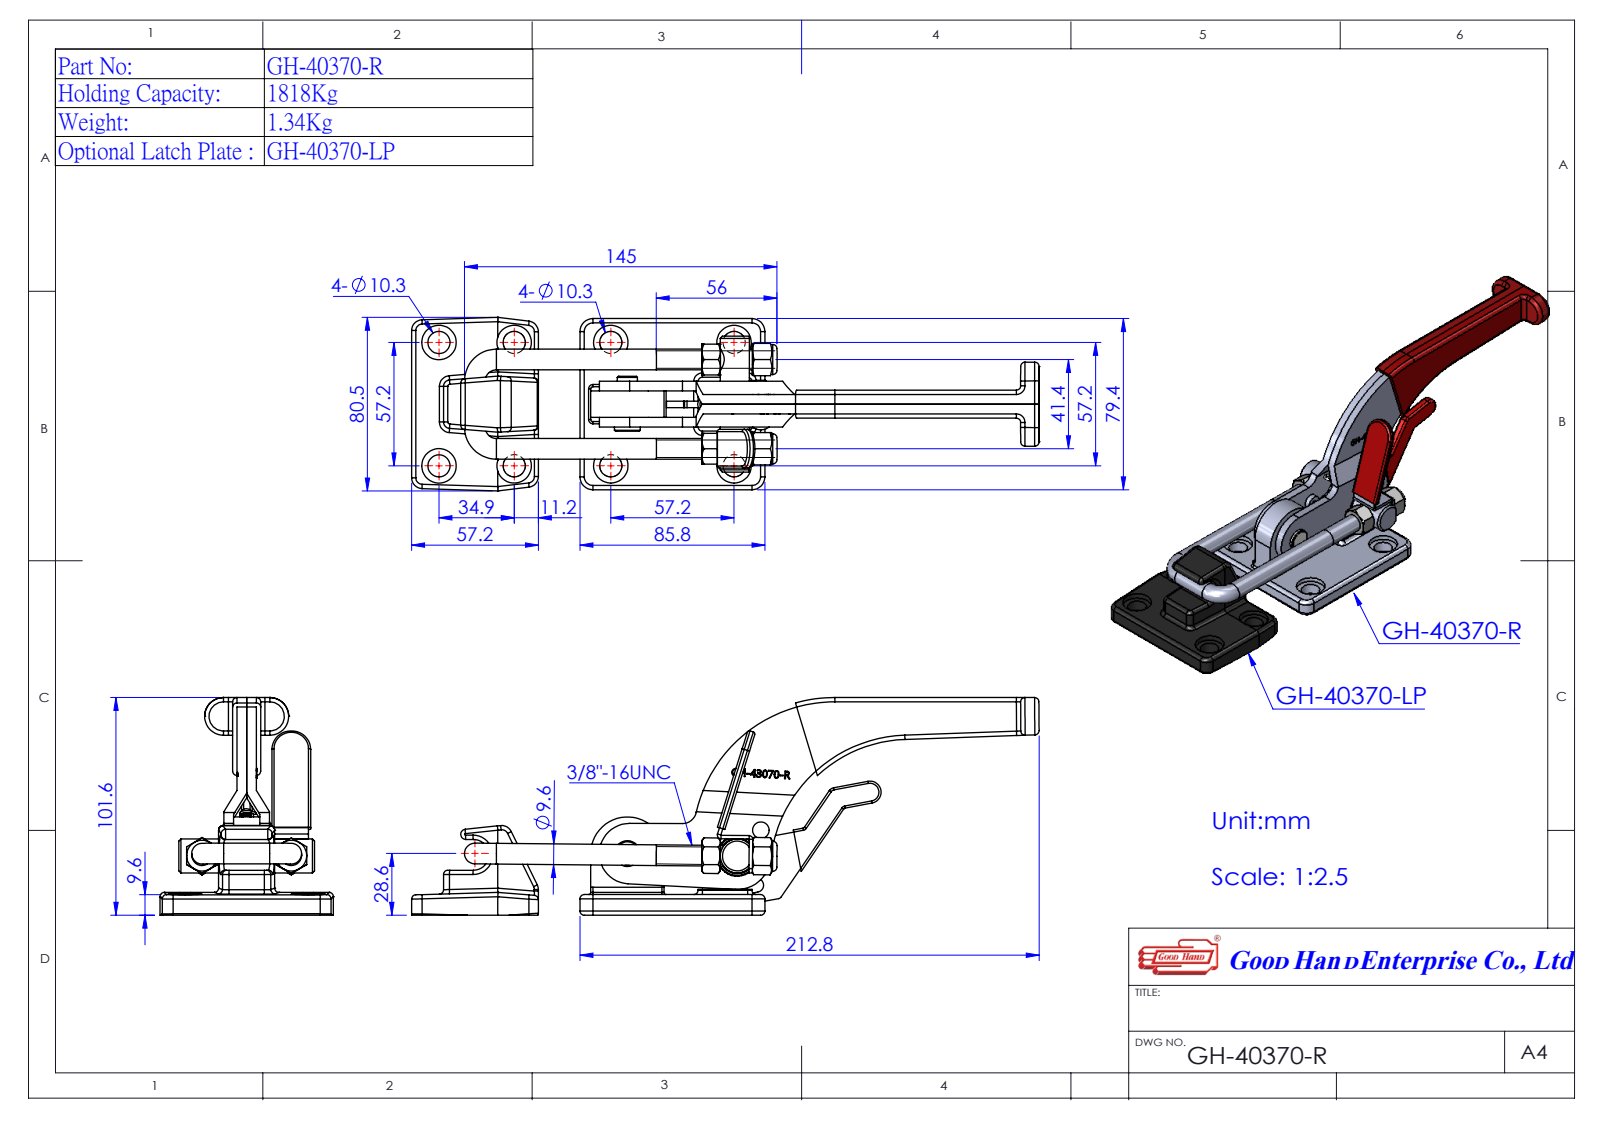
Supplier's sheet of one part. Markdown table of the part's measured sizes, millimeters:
| quantity | value |
| --- | --- |
| part name | Group1^GH-40370-R(簡化); GH-40370-R(簡化); Group5^GH-40370-R(簡化); 340370R13-3^GH-40370-R(簡化) (+1 more) |
| STEP written by | SolidWorks 2016 (AUTOMOTIVE_DESIGN) |
| units | millimeters |
| bodies | 7 solids, 342 faces (147 planar, 122 cylindrical, 73 other) |
| overall size | 266.67 × 100.99 × 79.4 |
| volume | 188 672 mm³ |
| surface area | 70 134 mm² |
| round holes (diameter × count) | 16 × 5, 7.94 × 4, 10.3 × 4, 9.53 × 2, 9.6 × 2, 8 × 1 |
| round bosses / shafts (diameter × count) | 9.6 × 3, 14 × 2, 15.8 × 1, 12 × 1, 9.4 × 1 |
| partial cylindrical surfaces (radius × count) | 2 × 16, 6 × 4, 1 × 3, 0.1 × 2, 1.7 × 2, 3 × 2, 2.4 × 1, 3.2 × 1 |
| main face-to-face distances | 4.5, 4.1, 0.4, 12.6, 16.7, 17.1, 6.1, 12.2, 1, 11 |
| hole center spacings | 41.4, 57.2, 80.89, 51.02 |
